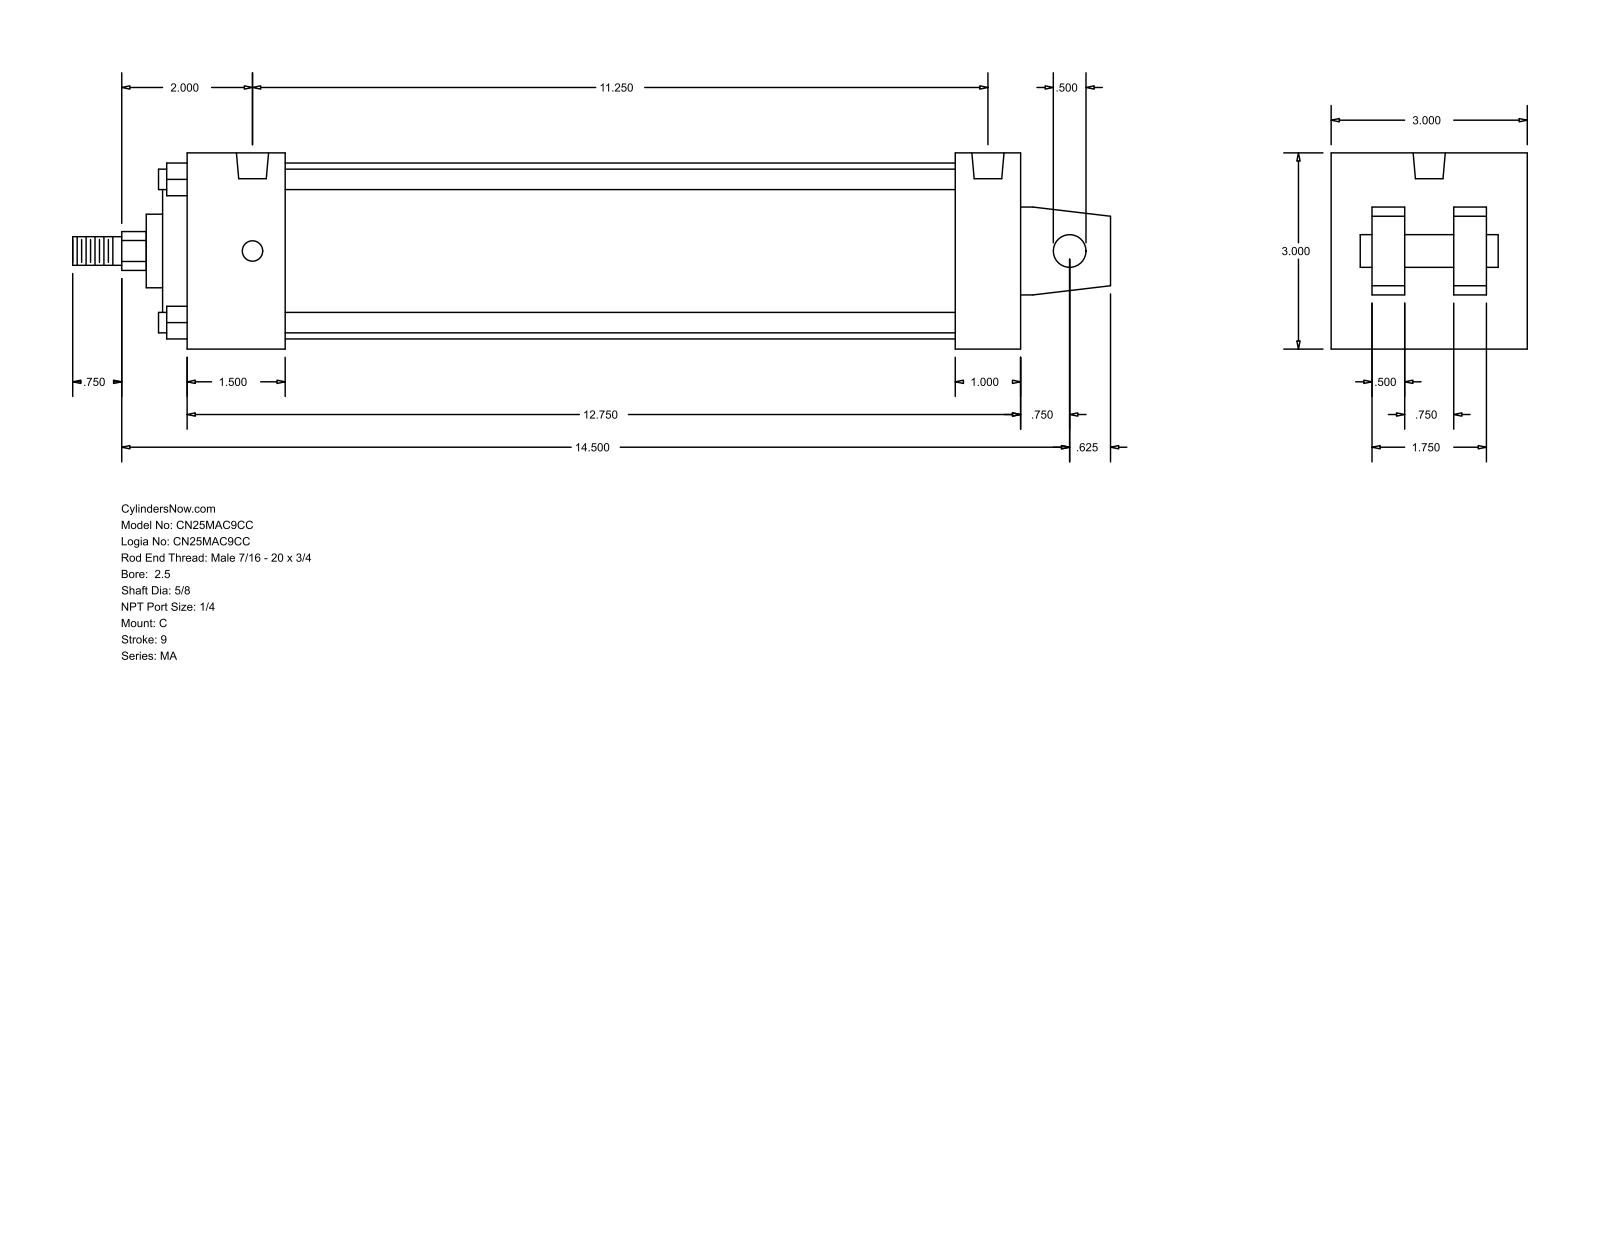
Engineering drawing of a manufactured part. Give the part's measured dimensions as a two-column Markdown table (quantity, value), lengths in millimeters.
| quantity | value |
| --- | --- |
| part name | MA_C__0250_0.625 |
| STEP written by | GSSL Pune (CONFIG_CONTROL_DESIGN) |
| units | millimeters |
| bodies | 0 solids, 105 faces (77 planar, 28 cylindrical, 0 other) |
| overall size | 403.23 × 76.2 × 76.2 |
| round holes (diameter × count) | 7.94 × 4, 12.49 × 2 |
| round bosses / shafts (diameter × count) | 7.94 × 4, 68.33 × 1, 50.8 × 1, 28.57 × 1, 15.88 × 1, 12.7 × 1, 11.11 × 1 |
| partial cylindrical surfaces (radius × count) | 7.54 × 1 |
| main face-to-face distances | 76.2, 323.85, 12.7, 15.87, 60.33, 47.63, 25.4, 38.1, 298.45, 260.35 |
| hole center spacings | 285.75 |
